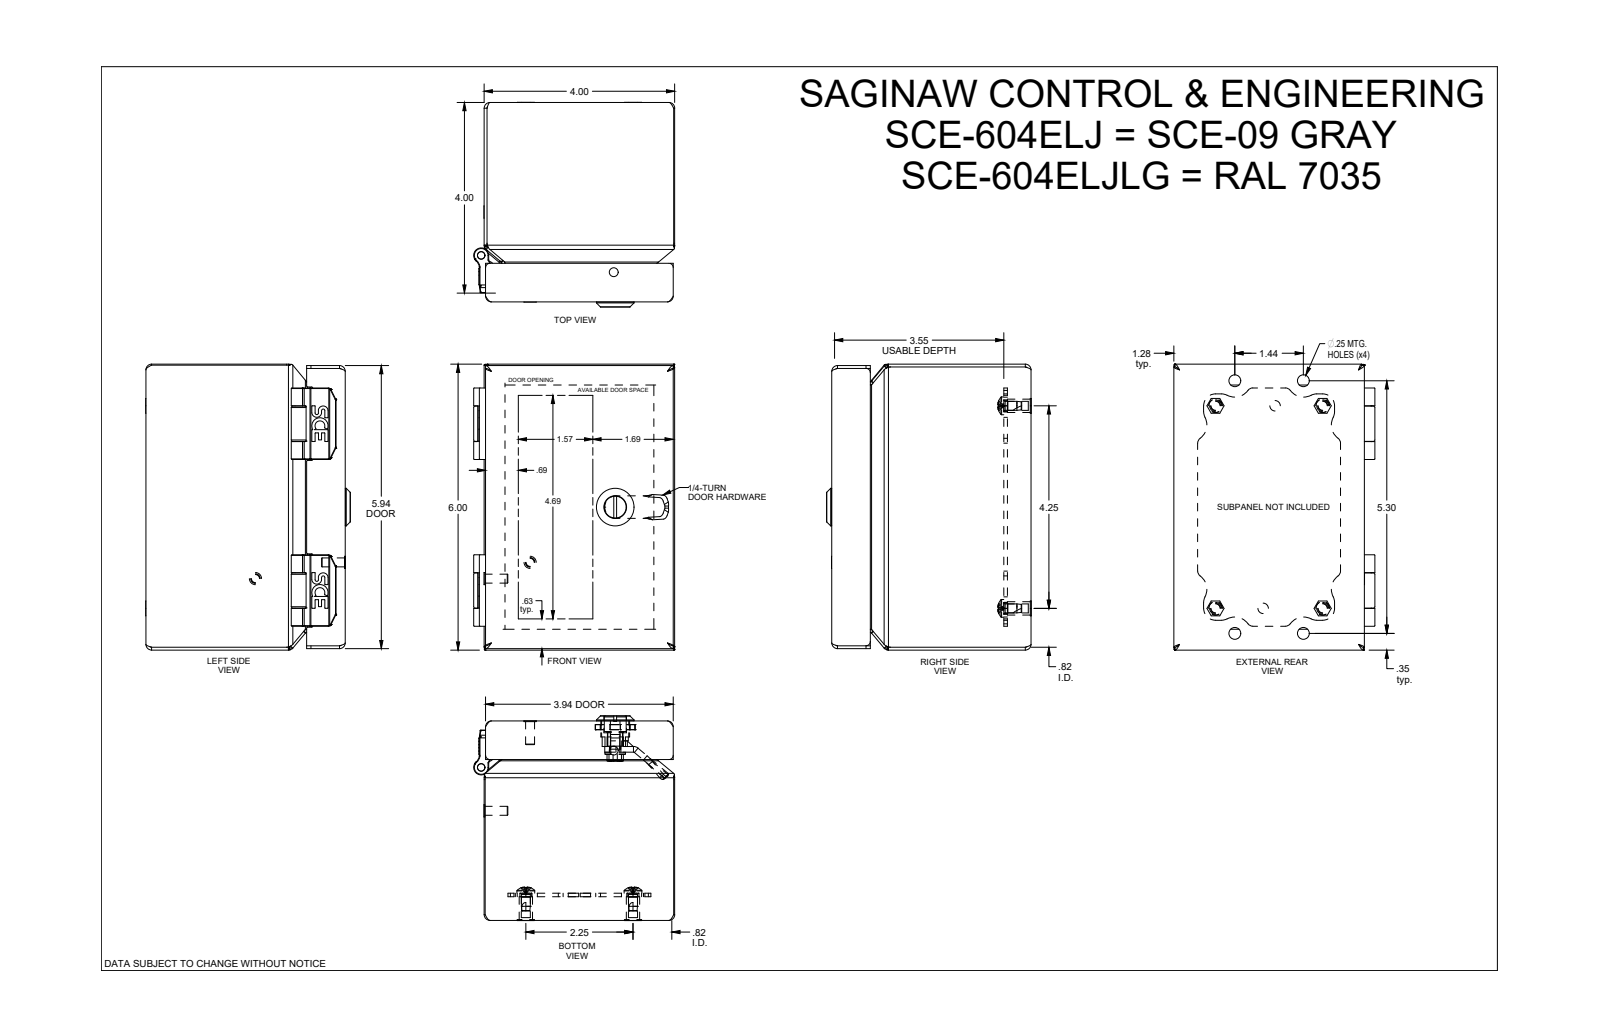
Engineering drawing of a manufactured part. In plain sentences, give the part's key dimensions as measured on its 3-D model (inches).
The part is named "SCE-604ELJ". Its 3-D file was written by "SolidWorks 2021 (AUTOMOTIVE_DESIGN)". It is 22 solids with 1294 faces: 401 planar, 390 cylindrical and 503 other. Overall it measures 6 by 4.292 by 4.22 inches. Its volume is 10.19 cubic inches and its surface area 330.2 square inches. Round holes: 8 of diameter 0.25, 4 of diameter 0.284, 2 of diameter 0.17, 2 of diameter 0.218, 1 of diameter 0.158, 1 of diameter 0.2, 1 of diameter 0.239, 1 of diameter 0.254, 1 of diameter 0.269, 1 of diameter 0.282, 1 of diameter 0.326, 1 of diameter 0.475. Round bosses or shafts: 5 of diameter 0.188, 4 of diameter 0.373, 4 of diameter 0.284, 2 of diameter 0.479, 2 of diameter 0.26, 2 of diameter 0.1, 2 of diameter 0.02, 1 of diameter 0.788. Partial cylindrical surfaces (rounded edges, fillets, slot ends): 66 of radius 0.106, 36 of radius 0.005, 32 of radius 0.008, 21 of radius 0.013, 16 of radius 0.05, 12 of radius 0.025, 12 of radius 0.25, 10 of radius 0.01. The main face-to-face distances are 0.059, 0.062, 3.941, 5.941, 4.123, 4.185, 4.126, 4.064, 4, 3.882. The hole center spacings are 0.664, 1.917, 2.25, 4.792, 5.119, 0.663, 0.793, 0.994.
